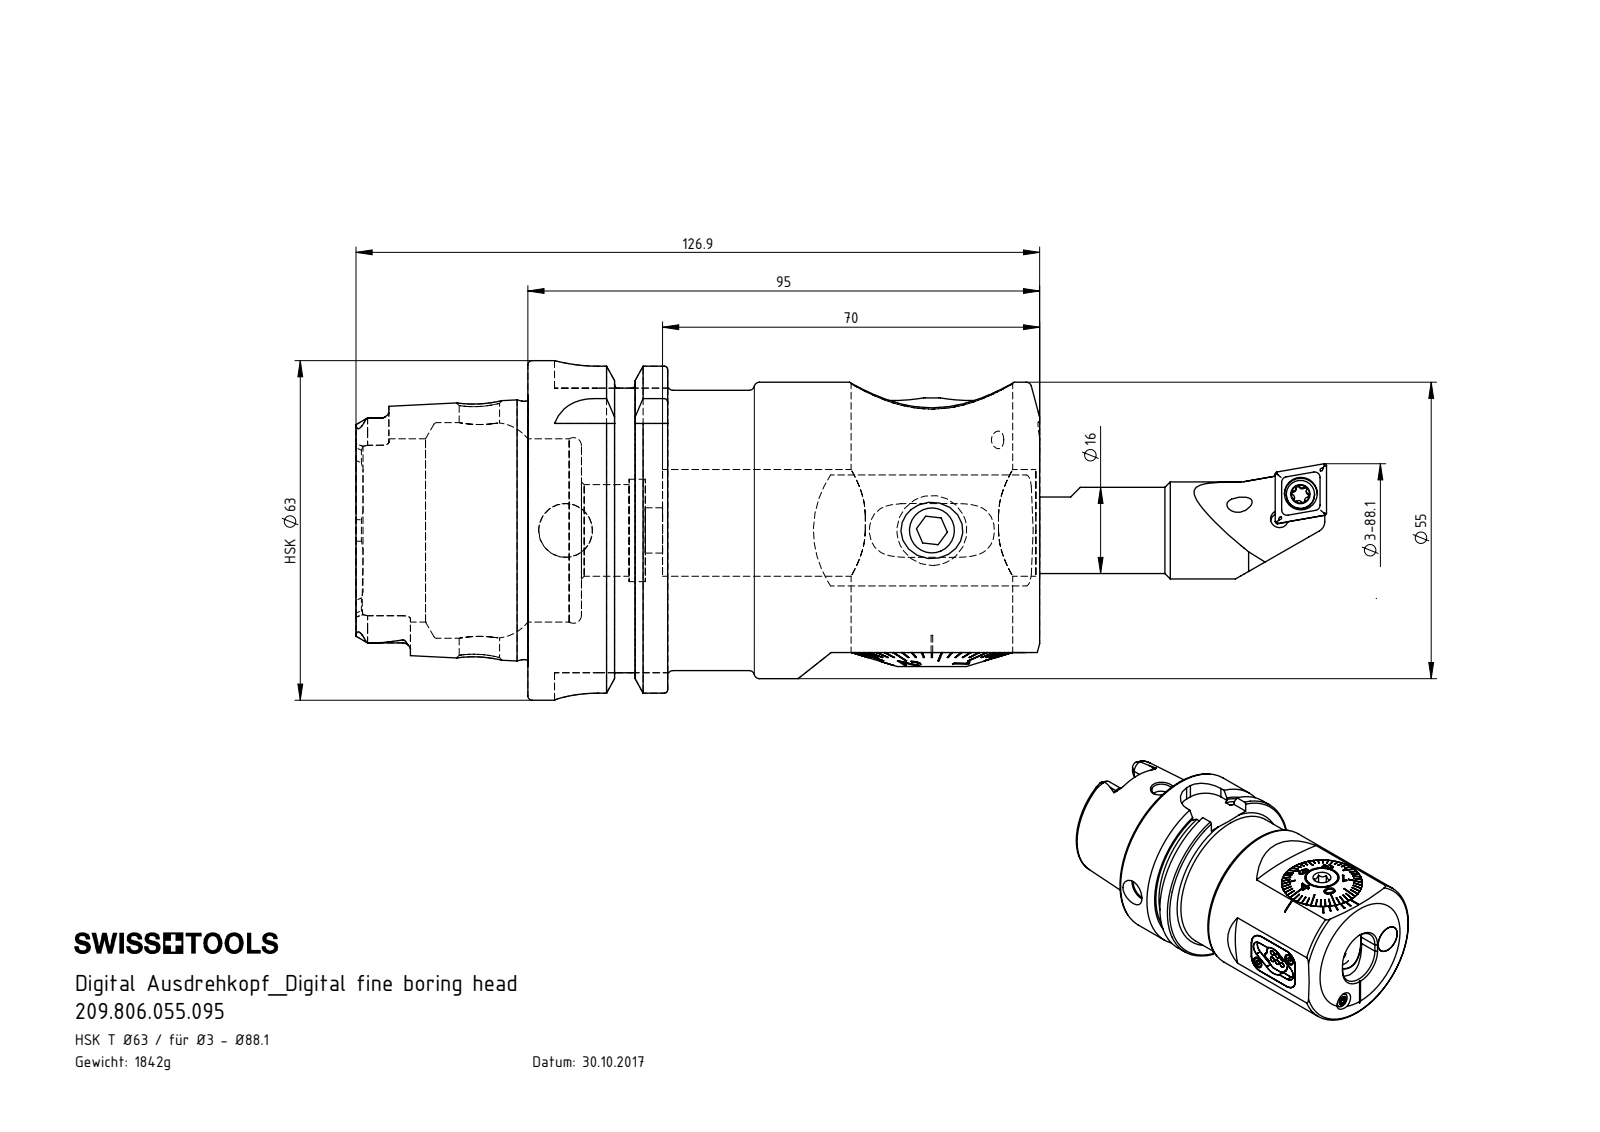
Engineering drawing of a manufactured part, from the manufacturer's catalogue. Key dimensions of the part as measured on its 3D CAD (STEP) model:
Part name (STEP PRODUCT): ISO 4026 - M10 x 8; B25-WCB.K11.115_B; B25-WCB.K11.115; A55-BG3.011.033_A_gekrzt (+8 more)
STEP written by: SolidWorks 2017 (CONFIG_CONTROL_DESIGN)
Units: millimetres
Bodies: 27 solids, 1268 faces (514 planar, 329 cylindrical, 425 other)
Overall size (bounding box): 180.15 × 63 × 63
Volume: 235 668 mm³ · Surface area: 68 956 mm²
Round holes (diameter × count): ⌀3.2 ×4, ⌀1.6 ×3, ⌀3.3 ×3, ⌀4.2 ×3, ⌀8.5 ×3, ⌀2.2 ×2, ⌀3 ×2, ⌀10 ×2, ⌀4.4 ×1, ⌀6.1 ×1, ⌀7.5 ×1, ⌀8 ×1
Round bosses / shafts (diameter × count): ⌀1.9 ×6, ⌀10 ×3, ⌀18 ×2, ⌀5.25 ×2, ⌀4 ×2, ⌀3.8 ×2, ⌀2 ×2, ⌀63 ×1
Partial cylindrical surfaces — rounded edges, fillets, slot ends (radius × count): R0.34 ×12, R0.59 ×12, R1.2 ×8, R1.1 ×6, R1.4 ×6, R2.88 ×4, R4.5 ×4, R8 ×4
Main face-to-face distances: 95, 16, 3.7, 2, 4, 25.95, 69.05, 9.95, 85.05, 5.3
Hole centre spacings: 4.1, 4.32, 7.25, 8.45, 9.52, 12, 12.68, 14.5
